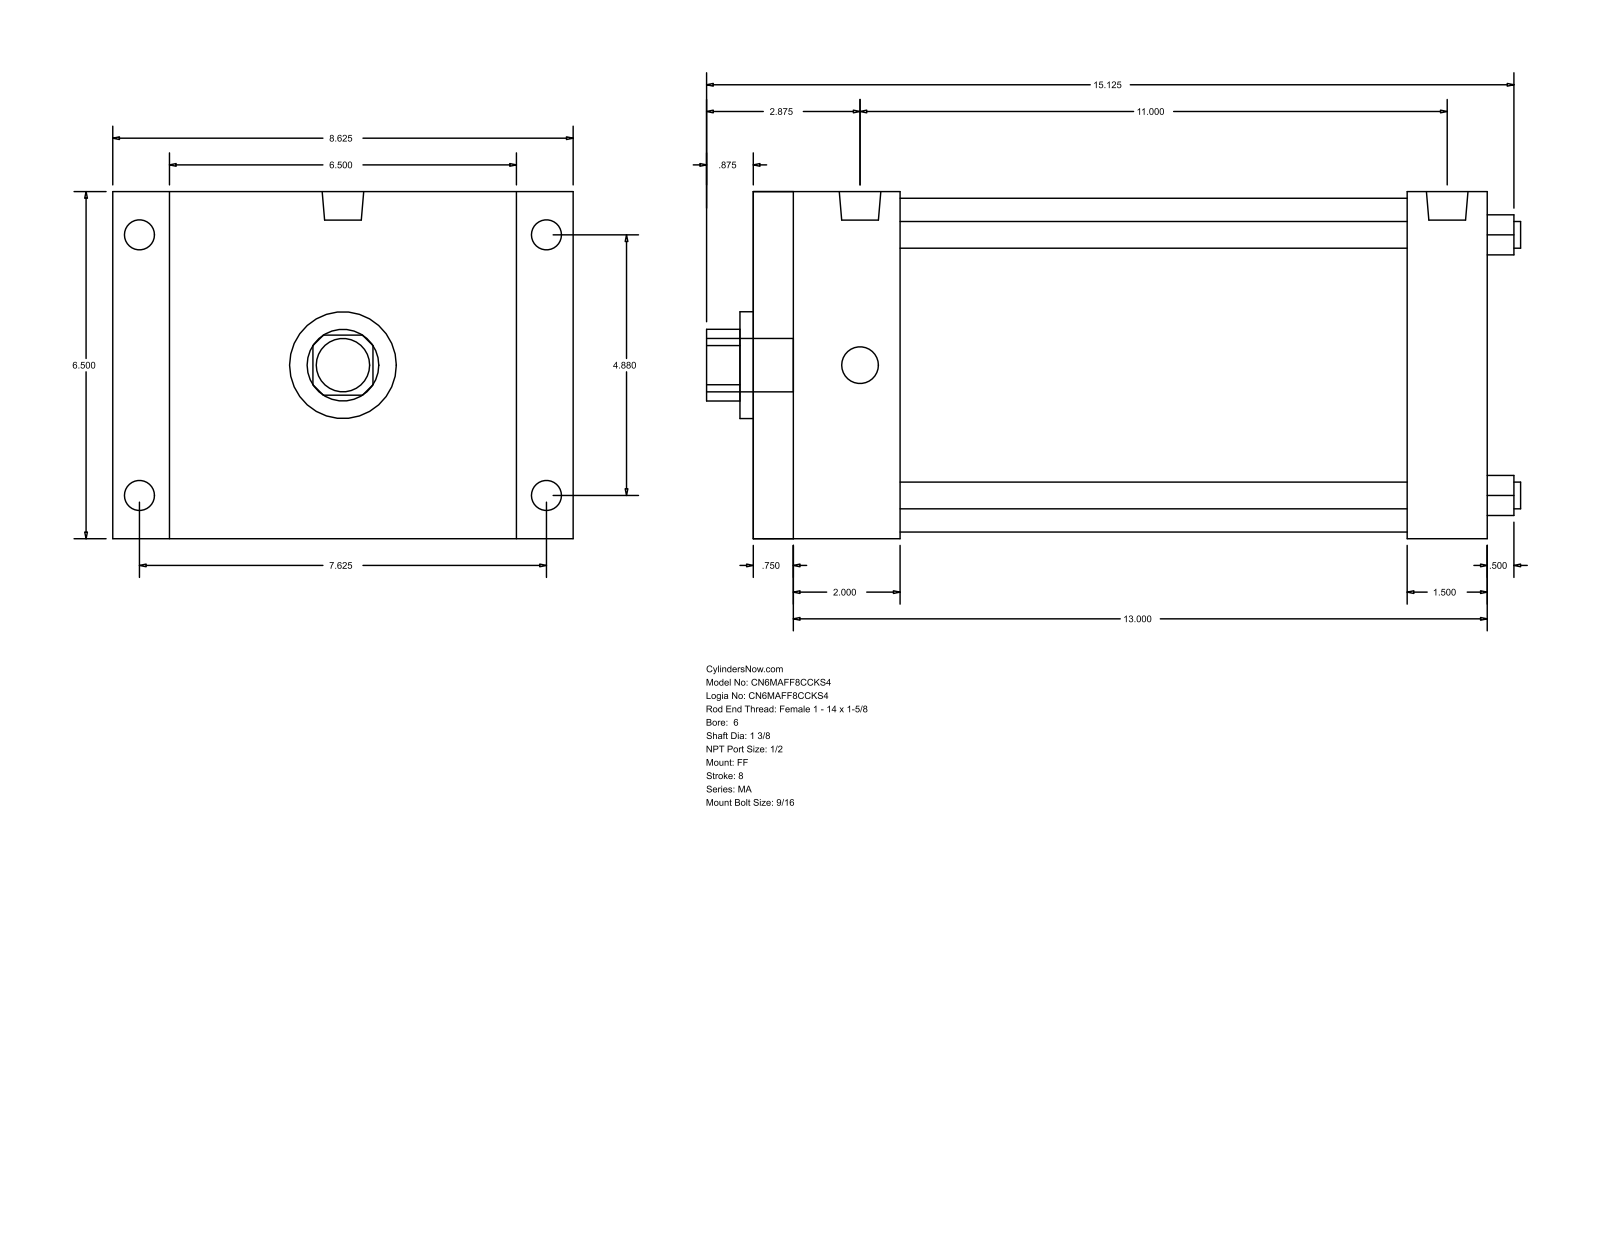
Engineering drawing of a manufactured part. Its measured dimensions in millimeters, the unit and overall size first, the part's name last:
Units: millimetres
Overall size (bounding box): 387.35 × 219.07 × 165.1
Round holes (diameter × count): ⌀12.7 ×4, ⌀34.92 ×1, ⌀50.8 ×1, ⌀158.75 ×1
Round bosses / shafts (diameter × count): ⌀17.46 ×4, ⌀14.29 ×4, ⌀19.77 ×2, ⌀25.4 ×1
Partial cylindrical surfaces — rounded edges, fillets, slot ends (radius × count): R17.06 ×1
Main face-to-face distances: 165.1, 349.25, 15.87, 333.38, 50.8, 295.28, 38.1, 66.67, 282.58, 311.15
Hole centre spacings: 87.65, 123.96, 175.31
Bodies: 0 solids, 92 faces (64 planar, 28 cylindrical, 0 other)
Part name (STEP PRODUCT): MA_FF__0600_1.375
STEP written by: GSSL Pune (CONFIG_CONTROL_DESIGN)
